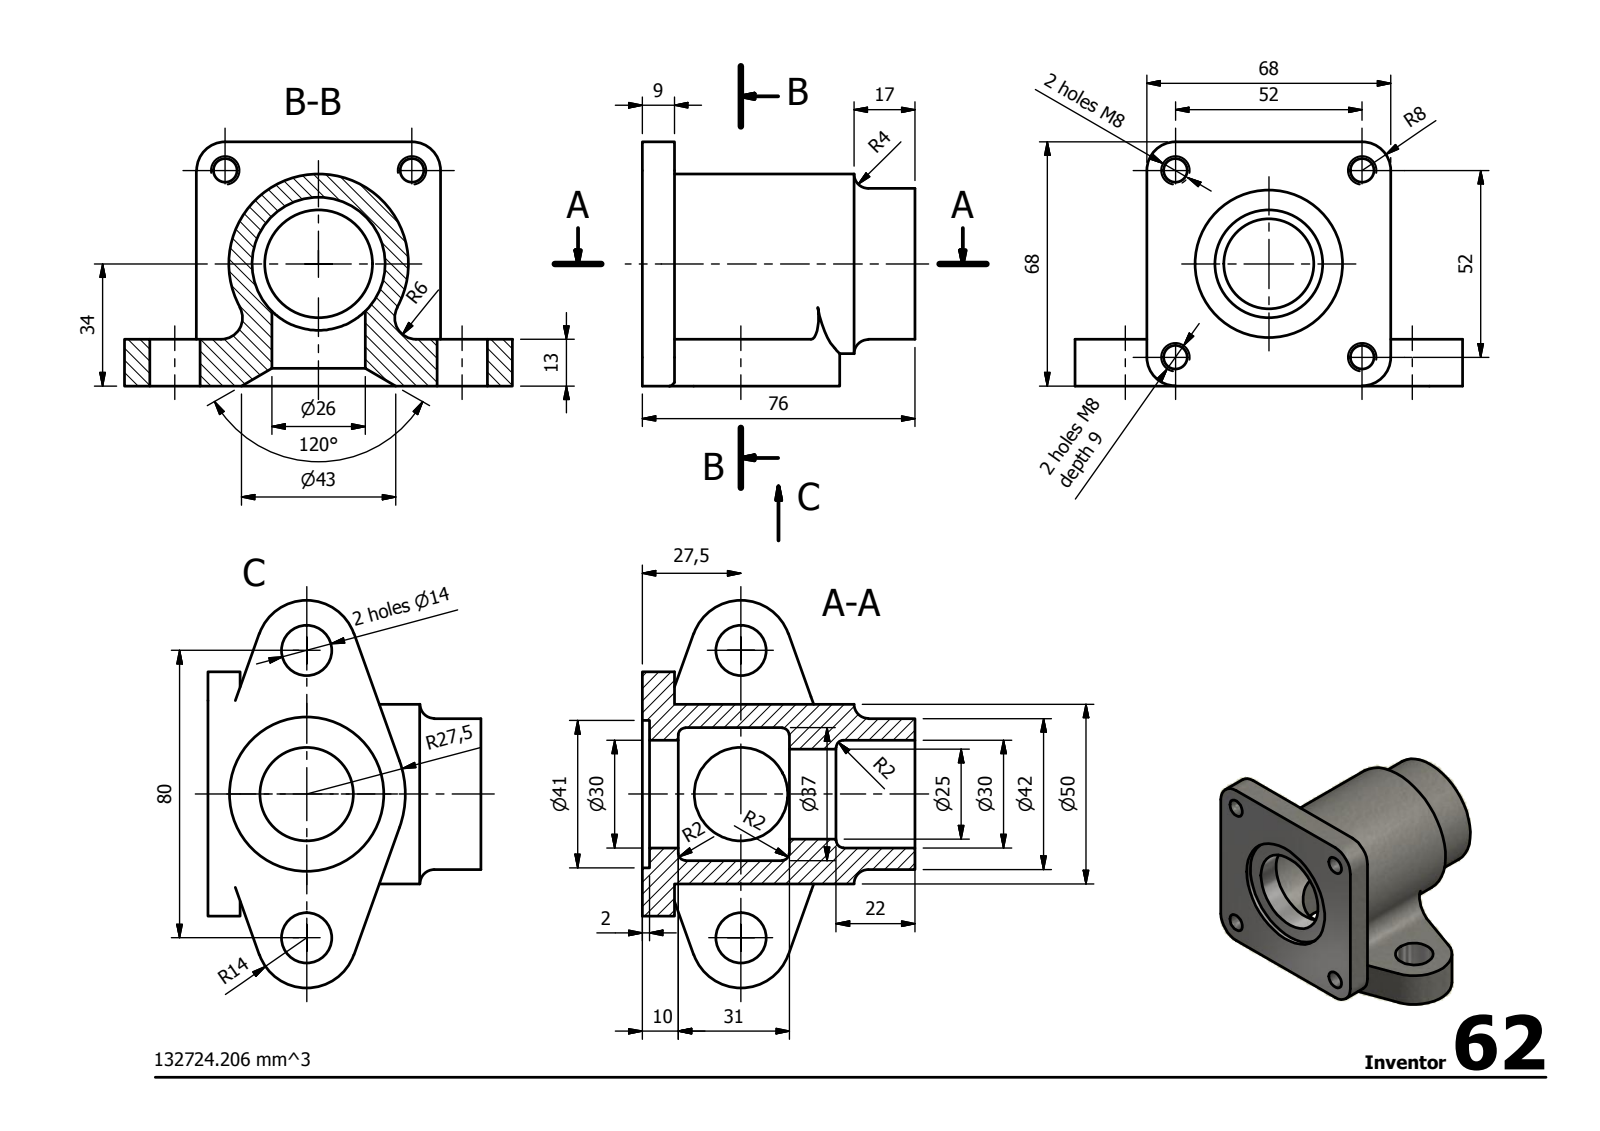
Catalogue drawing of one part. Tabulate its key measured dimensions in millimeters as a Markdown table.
| quantity | value |
| --- | --- |
| STEP written by | Autodesk Inventor 2014 (AUTOMOTIVE_DESIGN) |
| units | millimeters |
| bodies | 1 solid, 47 faces (17 planar, 23 cylindrical, 7 other) |
| overall size | 108 × 76 × 68 |
| volume | 132 726 mm³ |
| surface area | 35 551 mm² |
| round holes (diameter × count) | 6.65 × 4, 14 × 2, 25 × 1, 26 × 1, 30 × 1, 37 × 1, 41 × 1 |
| round bosses / shafts (diameter × count) | 50 × 1, 42 × 1 |
| partial cylindrical surfaces (radius × count) | 8 × 4, 6 × 2, 14 × 2, 27.5 × 1 |
| main face-to-face distances | 9, 13, 68, 76, 67, 2, 7, 74, 55, 41 |
| hole center spacings | 36.77, 52, 40, 73.54, 80 |
